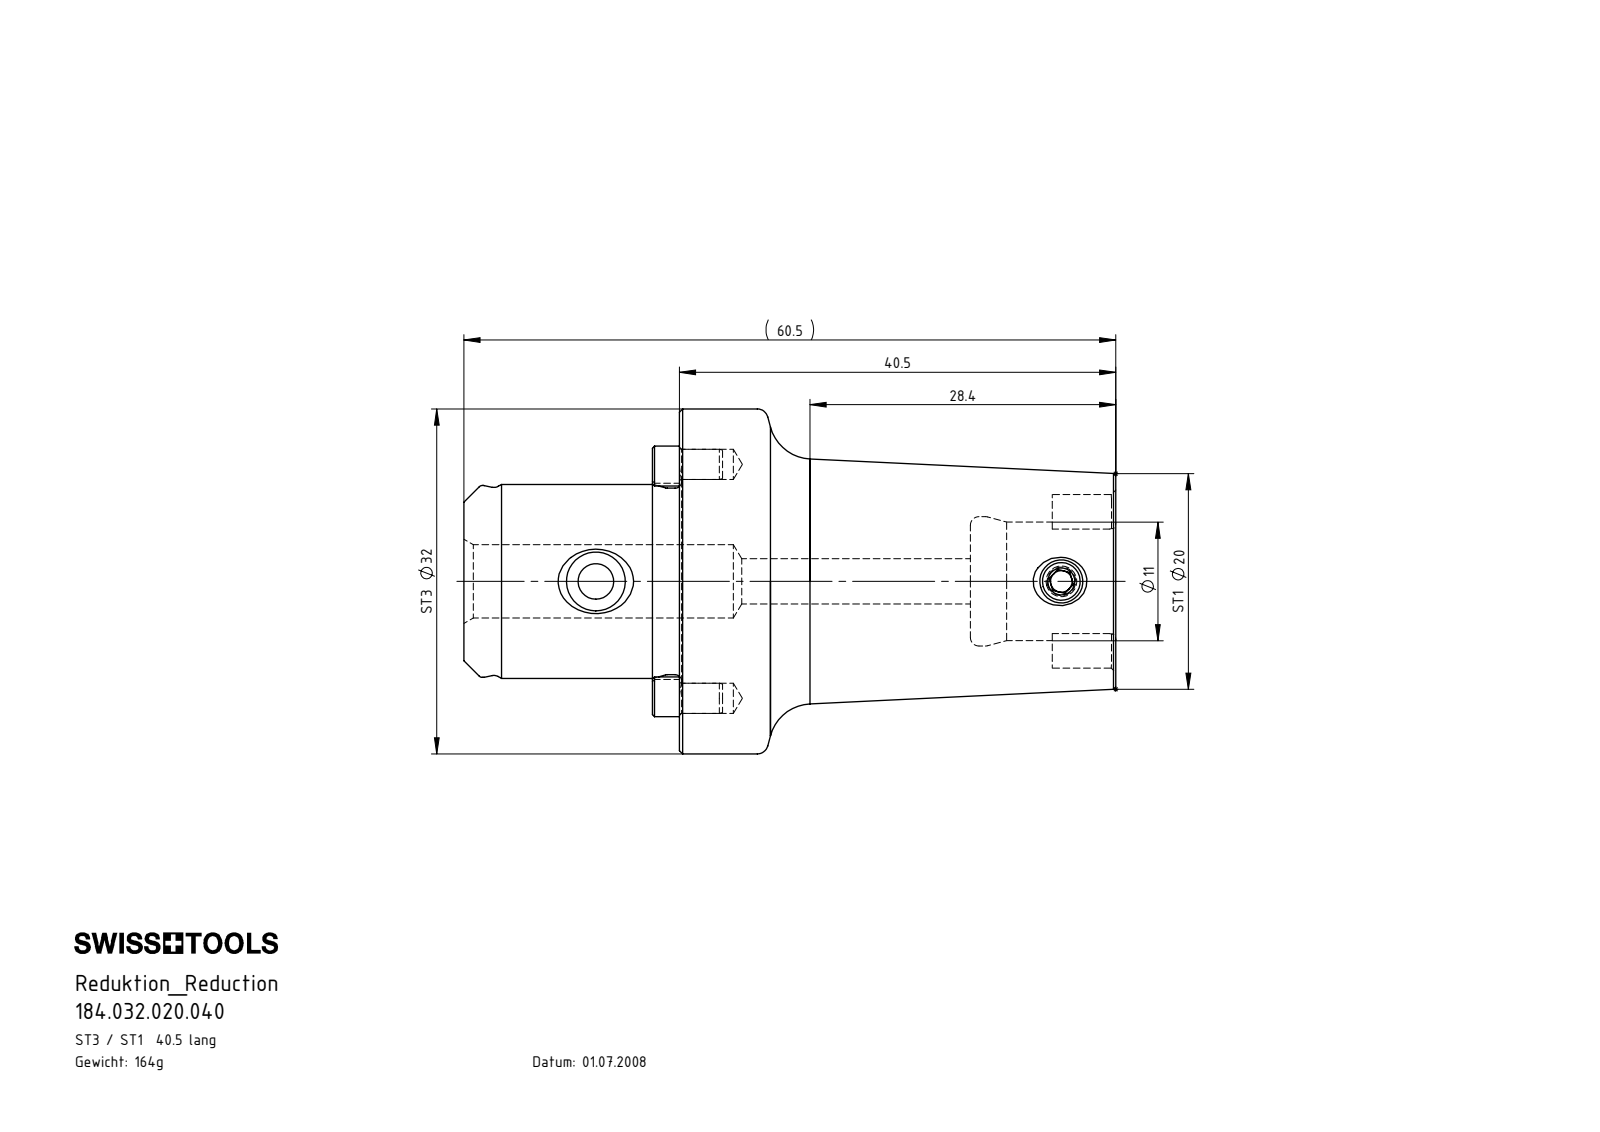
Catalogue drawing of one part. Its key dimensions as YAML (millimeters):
part_name: "ST3-ER2.001.007_A; ST3-ST1.K01.040_A; ST1-ER1.001.005_A; ST3-ST1.K01.040"
step_written_by: "SolidWorks 2015 (CONFIG_CONTROL_DESIGN)"
units: millimeters
bodies: {solids: 4, faces: 162, planar: 26, cylindrical: 45, other: 91}
overall_size: [60.5, 32, 32]
volume: 20918
surface_area: 7178
round_holes:
  - {diameter: 2.8, count: 2}
  - {diameter: 3.3, count: 1}
  - {diameter: 3.5, count: 1}
  - {diameter: 4.2, count: 1}
  - {diameter: 6.8, count: 1}
  - {diameter: 11, count: 1}
  - {diameter: 12, count: 1}
round_bosses_or_shafts:
  - {diameter: 32, count: 1}
  - {diameter: 18, count: 1}
  - {diameter: 17.8, count: 1}
  - {diameter: 17.3, count: 1}
  - {diameter: 4, count: 1}
partial_cylinders:
  - {radius: 0.5, count: 4}
  - {radius: 1.3, count: 2}
  - {radius: 2.73, count: 2}
  - {radius: 9.05, count: 2}
face_to_face_distances: [40.5, 20, 60.5, 47, 27, 13.5, 9.34, 17.5, 2.5, 29.5]
hole_center_spacings: [10.85, 21.7, 43.2]
